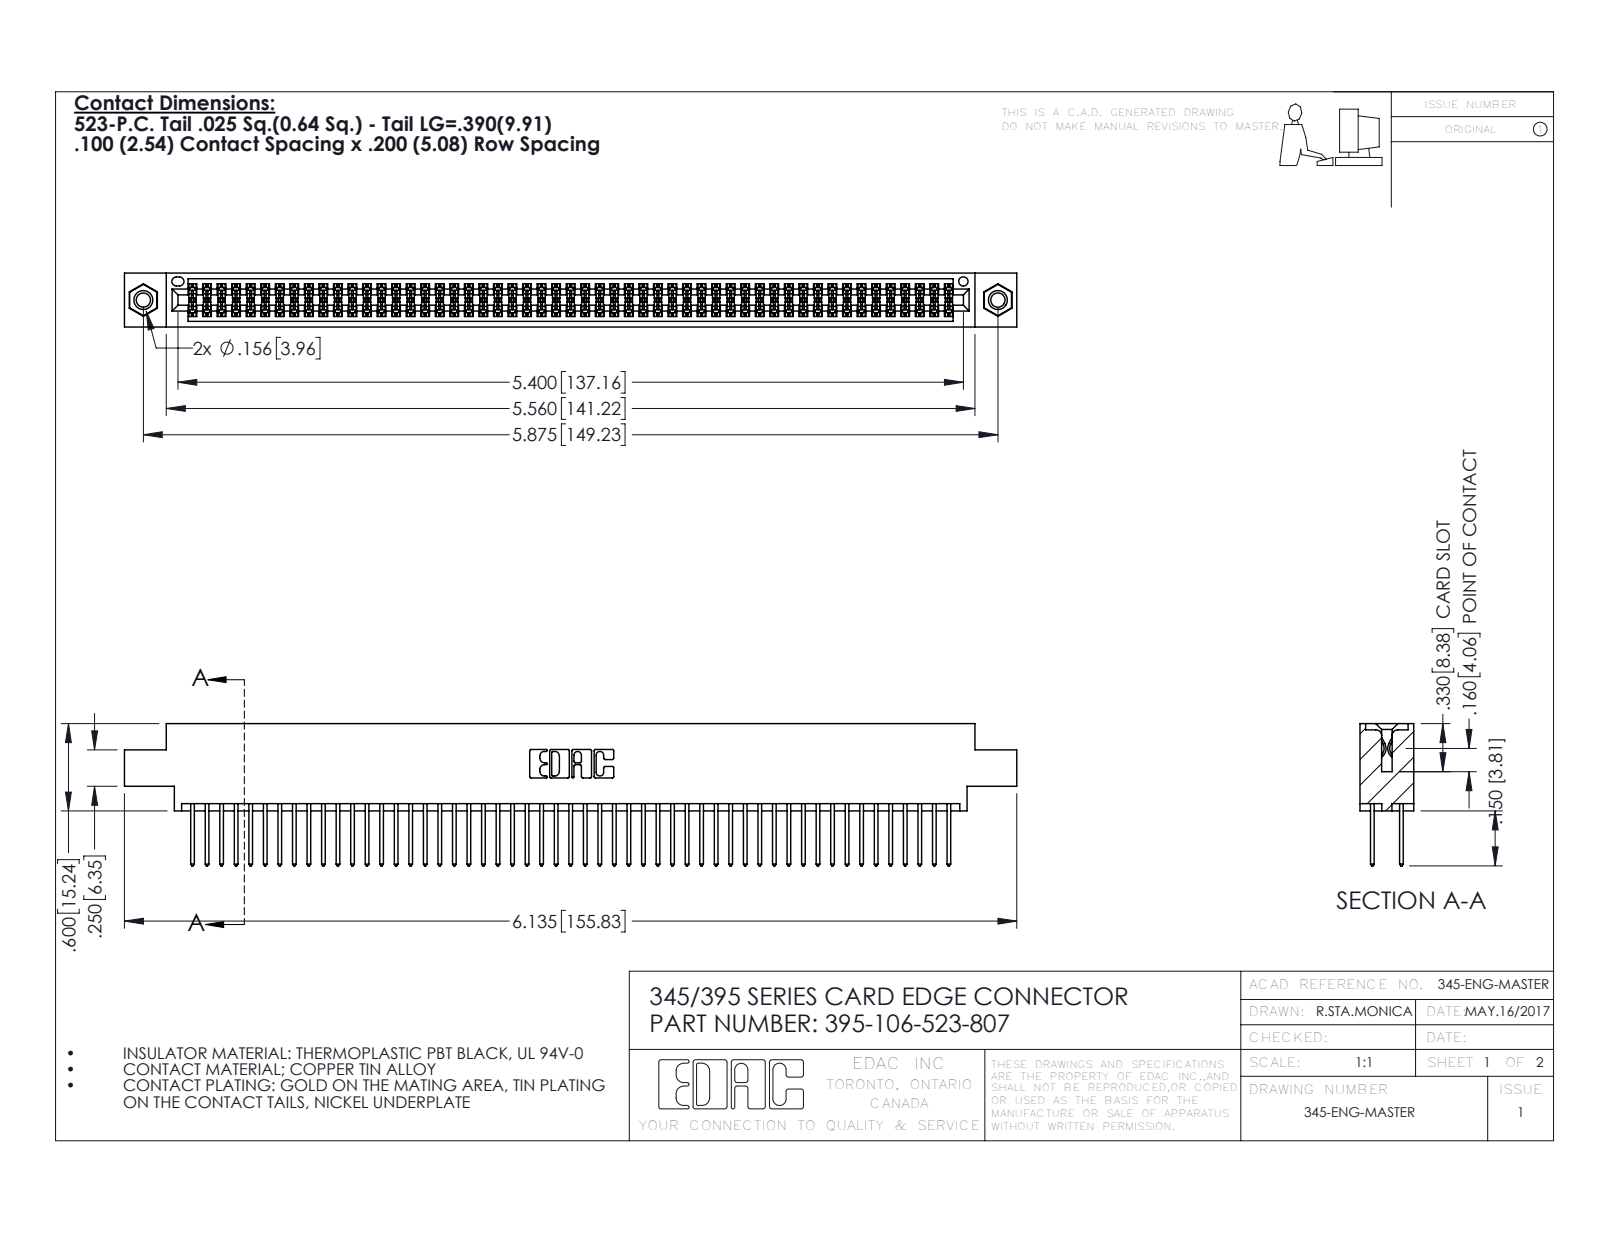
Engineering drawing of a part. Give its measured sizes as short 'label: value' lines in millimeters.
name: 395-106-523-807; 345-250-001_345-250-005-103; 345 Part_0.170 Offset - 0.156 Dia-TI; 345-292-001_345-293-123
written by: SolidWorks 2016 (CONFIG_CONTROL_DESIGN)
unit: mm
bodies: 109 solids, 5490 faces (3614 planar, 1860 cylindrical, 16 other)
size: 155.8 × 24.8 × 9.4
volume: 15 300 mm³; area: 24 020 mm²
holes: 2× ⌀2.5, 2× ⌀3.2, 2× ⌀4, 1× ⌀1.6
bosses: 2× ⌀3.9
rounds: 159× R0.2, 106× R0.3, 22× R0.3, 6× R0.2, 6× R0.8, 3× R0.7, 2× R0.4, 2× R0.5
face distances: 1.8, 7.6, 5.1, 2.5, 6.9, 0.6, 9.4, 5.7, 4.4, 3.8
hole spacings: 6.9, 143.2, 149.2
